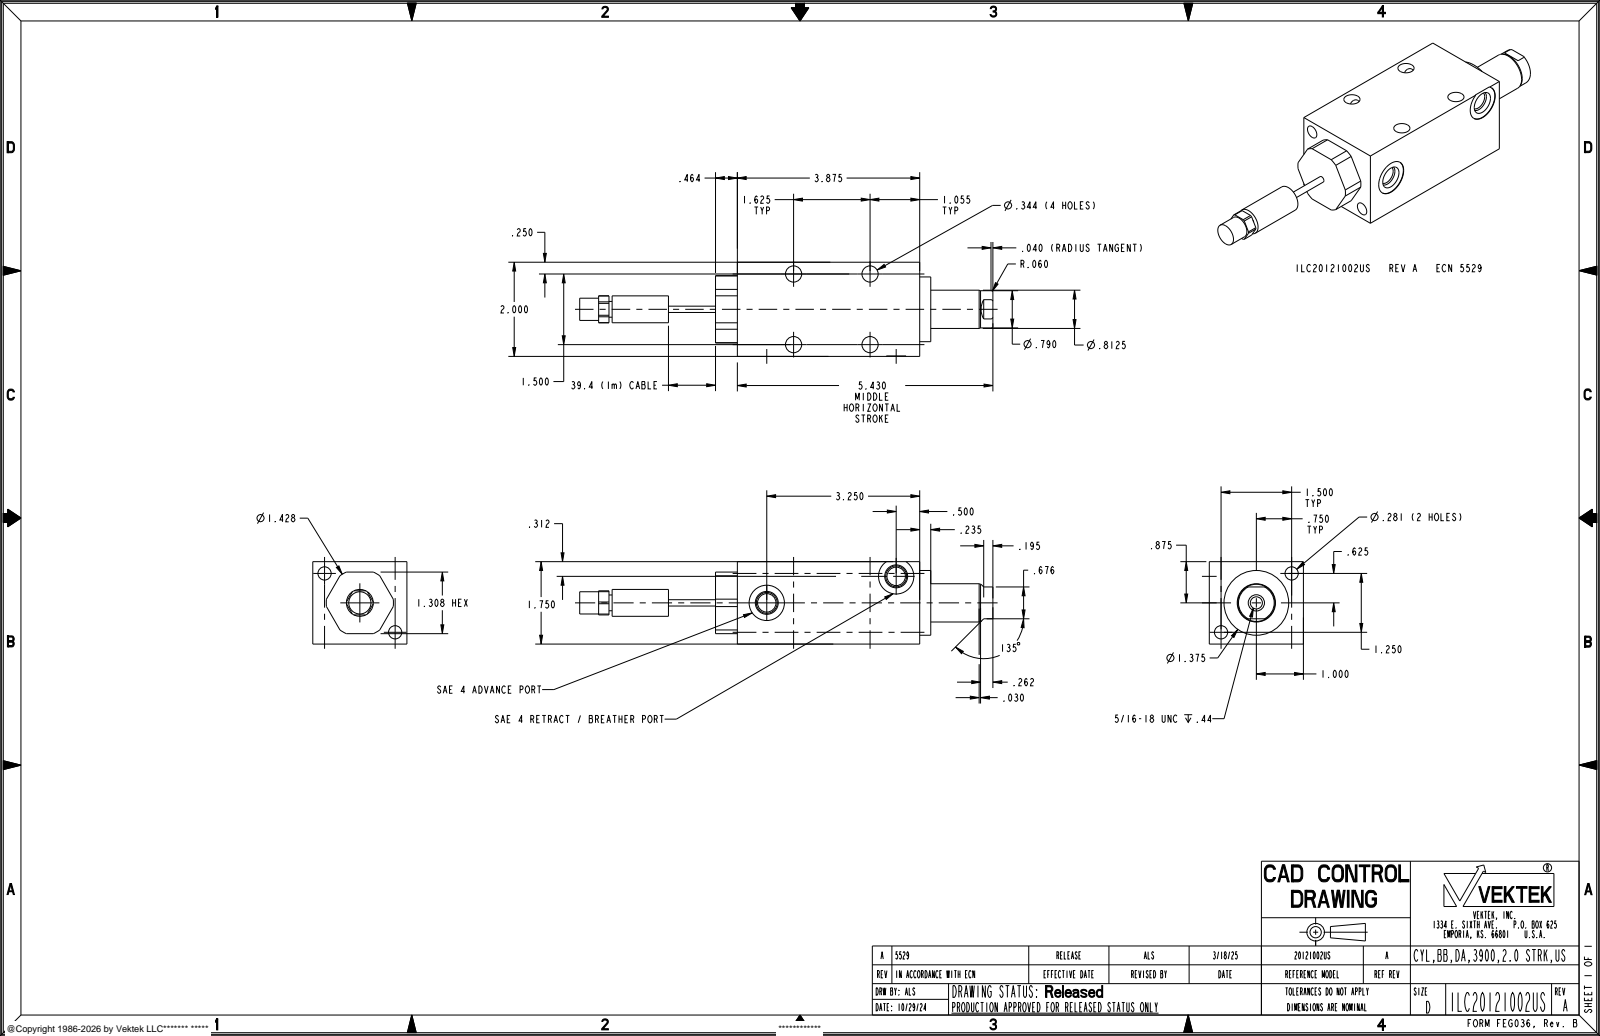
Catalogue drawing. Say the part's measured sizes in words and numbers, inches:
The part is named "ILC20121002US". Its 3-D file was written by "CREO PARAMETRIC BY PTC INC, 2021164 (AUTOMOTIVE_DESIGN)". It is 1 solid with 107 faces: 36 planar, 57 cylindrical and 14 other. Overall it measures 8.78 by 2.25 by 1.75 inches. Its volume is 14.47 cubic inches and its surface area 60.89 square inches. Round holes: 4 of diameter 0.344, 2 of diameter 0.281, 2 of diameter 0.392, 2 of diameter 0.75, 1 of diameter 0.257. Round bosses or shafts: 1 of diameter 1.375, 1 of diameter 0.813, 1 of diameter 0.79, 1 of diameter 0.571, 1 of diameter 0.472, 1 of diameter 0.335, 1 of diameter 0.312, 1 of diameter 0.134. Partial cylindrical surfaces (rounded edges, fillets, slot ends): 1 of radius 0.714. The main face-to-face distances are 1.75, 2, 3.875, 4.339, 0.464, 0.235, 4.11, 4.574, 1.308, 0.221. The hole center spacings are 0.976, 1.5, 1.625, 2.211, 1.953, 2.807.
